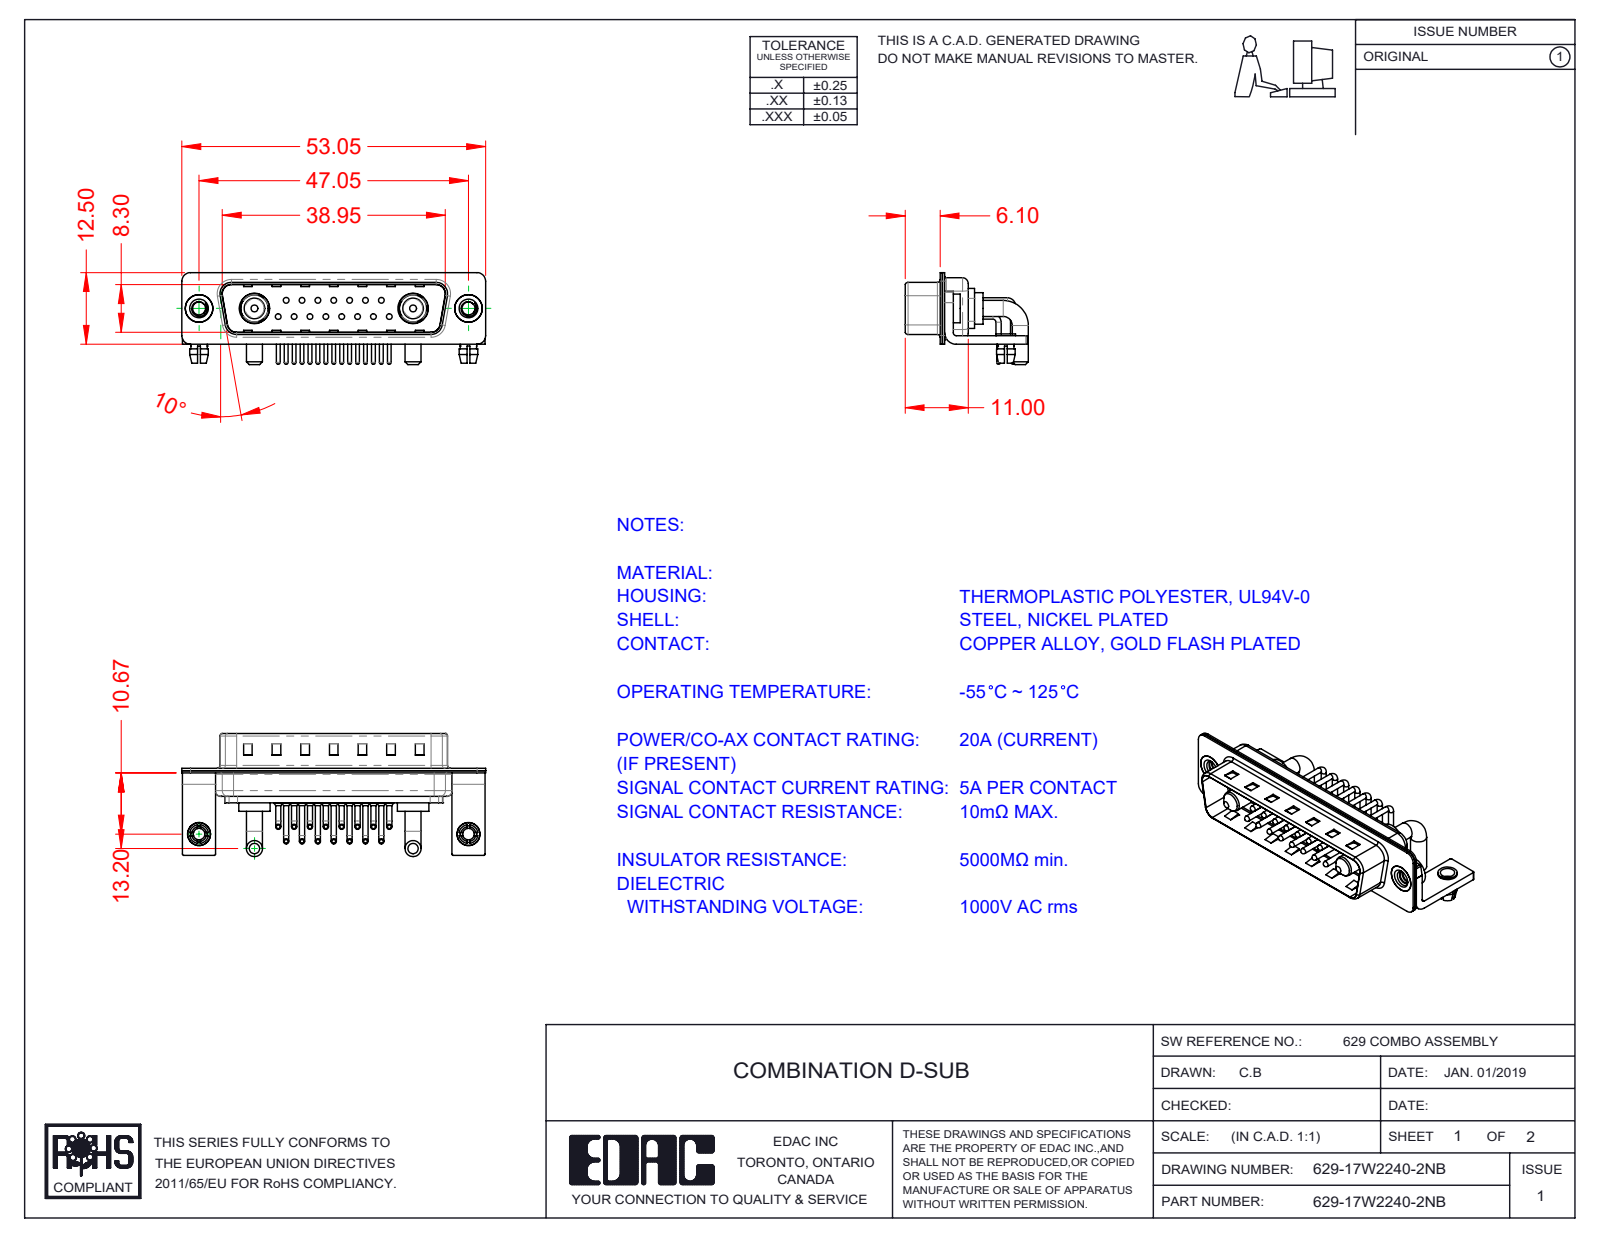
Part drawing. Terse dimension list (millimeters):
name: 629Combo Board Lock; 629Combo Housing_17W2; 629Combo Shell Front_25 Contacts; 629Combo Contact Row 1 (+6 more)
written by: SolidWorks 2020 (CONFIG_CONTROL_DESIGN)
unit: mm
bodies: 28 solids, 2252 faces (1219 planar, 775 cylindrical, 258 other)
size: 53.05 × 21.5 × 16.05
volume: 3 460 mm³; area: 8 328 mm²
holes: 17× ⌀2, 15× ⌀0.75, 15× ⌀1.6, 2× ⌀2.26, 2× ⌀2.5, 2× ⌀3.2, 2× ⌀4, 2× ⌀4.8, 2× ⌀4.85, 2× ⌀5.3
bosses: 30× ⌀0.9, 15× ⌀1.5, 15× ⌀1, 15× ⌀0.65, 4× ⌀2.8, 2× ⌀5.5, 2× ⌀5.2, 2× ⌀5
rounds: 16× R0.25, 16× R1.5, 15× R1.01, 13× R2, 9× R0.5, 8× R1.6, 4× R0.6, 4× R0.65
face distances: 0.4, 0.8, 9.5, 1.5, 9.1, 8.7, 9.9, 0.6, 1.2, 5.2
hole spacings: 3.16, 2.77, 5.54, 8.31, 5.04, 7.49, 11.08, 5.03
